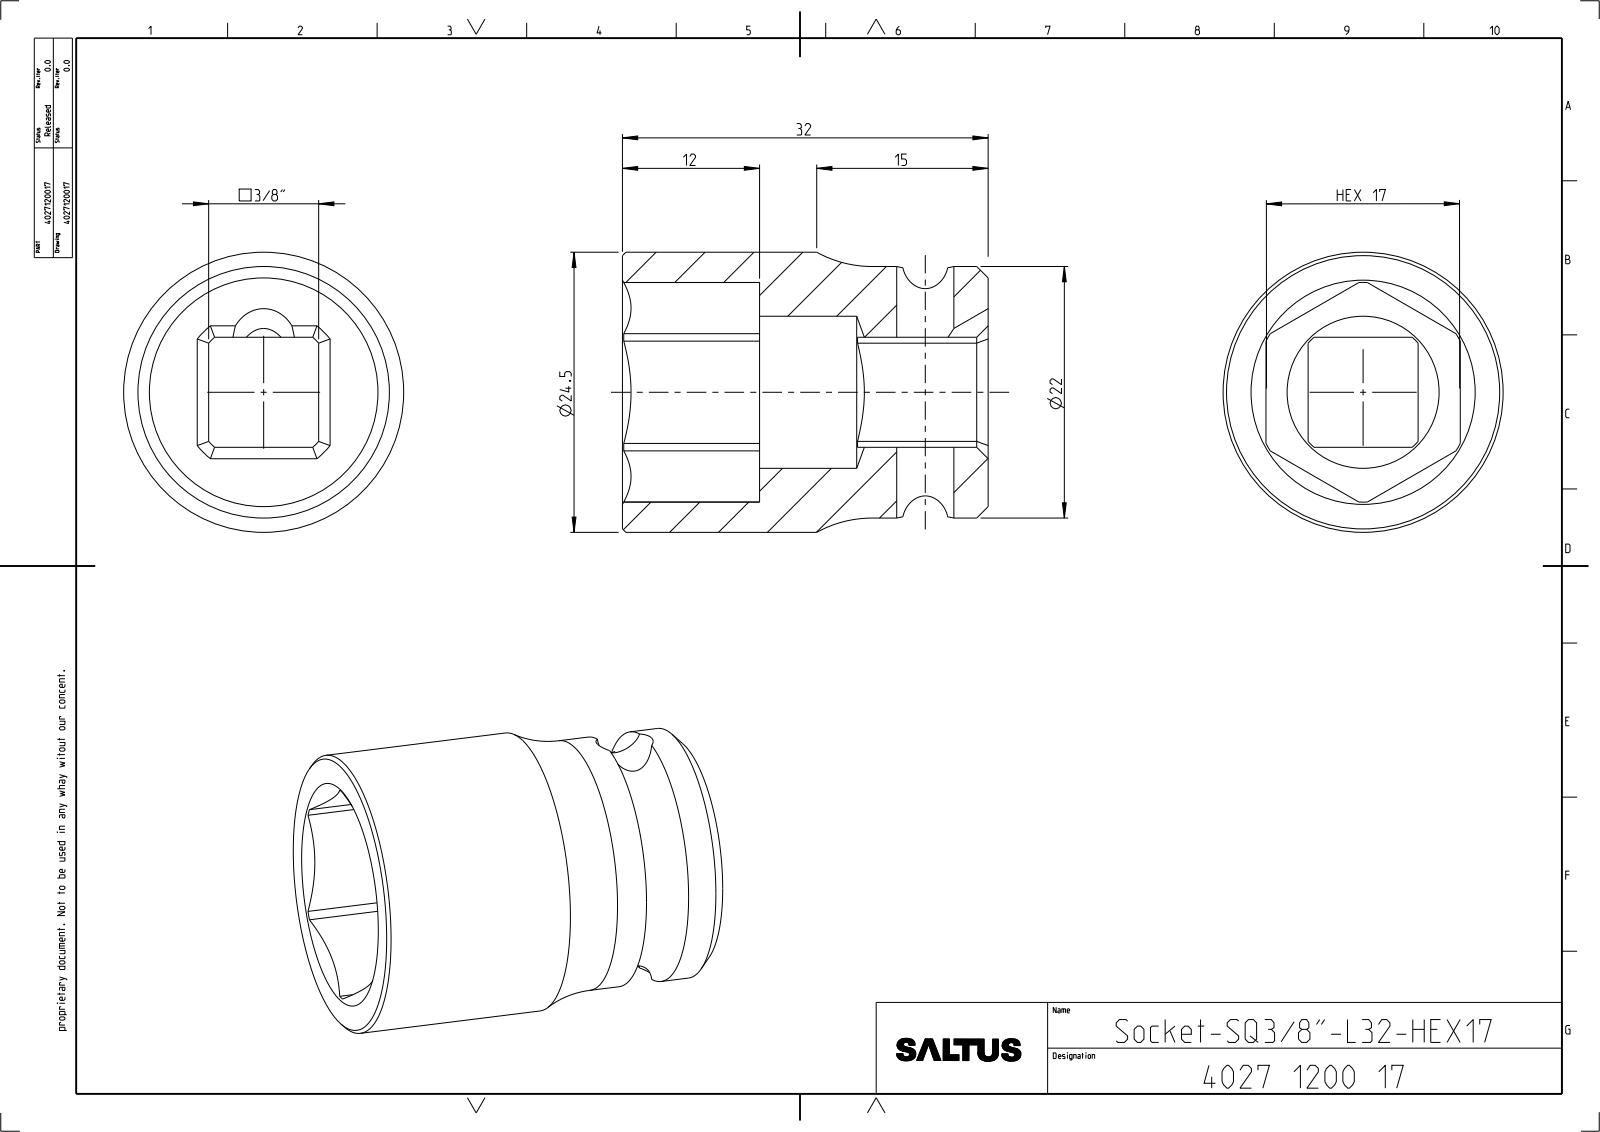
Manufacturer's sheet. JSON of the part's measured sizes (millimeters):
{"part_name": "4027120017", "step_written_by": "CREO PARAMETRIC BY PTC INC, 2022414 (CONFIG_CONTROL_DESIGN)", "units": "millimeters", "bodies": {"solids": 1, "faces": 57, "planar": 18, "cylindrical": 23, "other": 16}, "overall_size": [32, 24.5, 24.5], "volume_mm3": 8018, "surface_area_mm2": 4560, "round_holes": [[5, 1], [13.3, 1]], "round_bosses_or_shafts": [[24.5, 1], [22, 1]], "partial_cylinders_radius": [[3, 1], [6.45, 1], [9.61, 1]], "face_to_face_distances": [17, 3.69, 13.31, 32, 9.62, 20, 12]}
